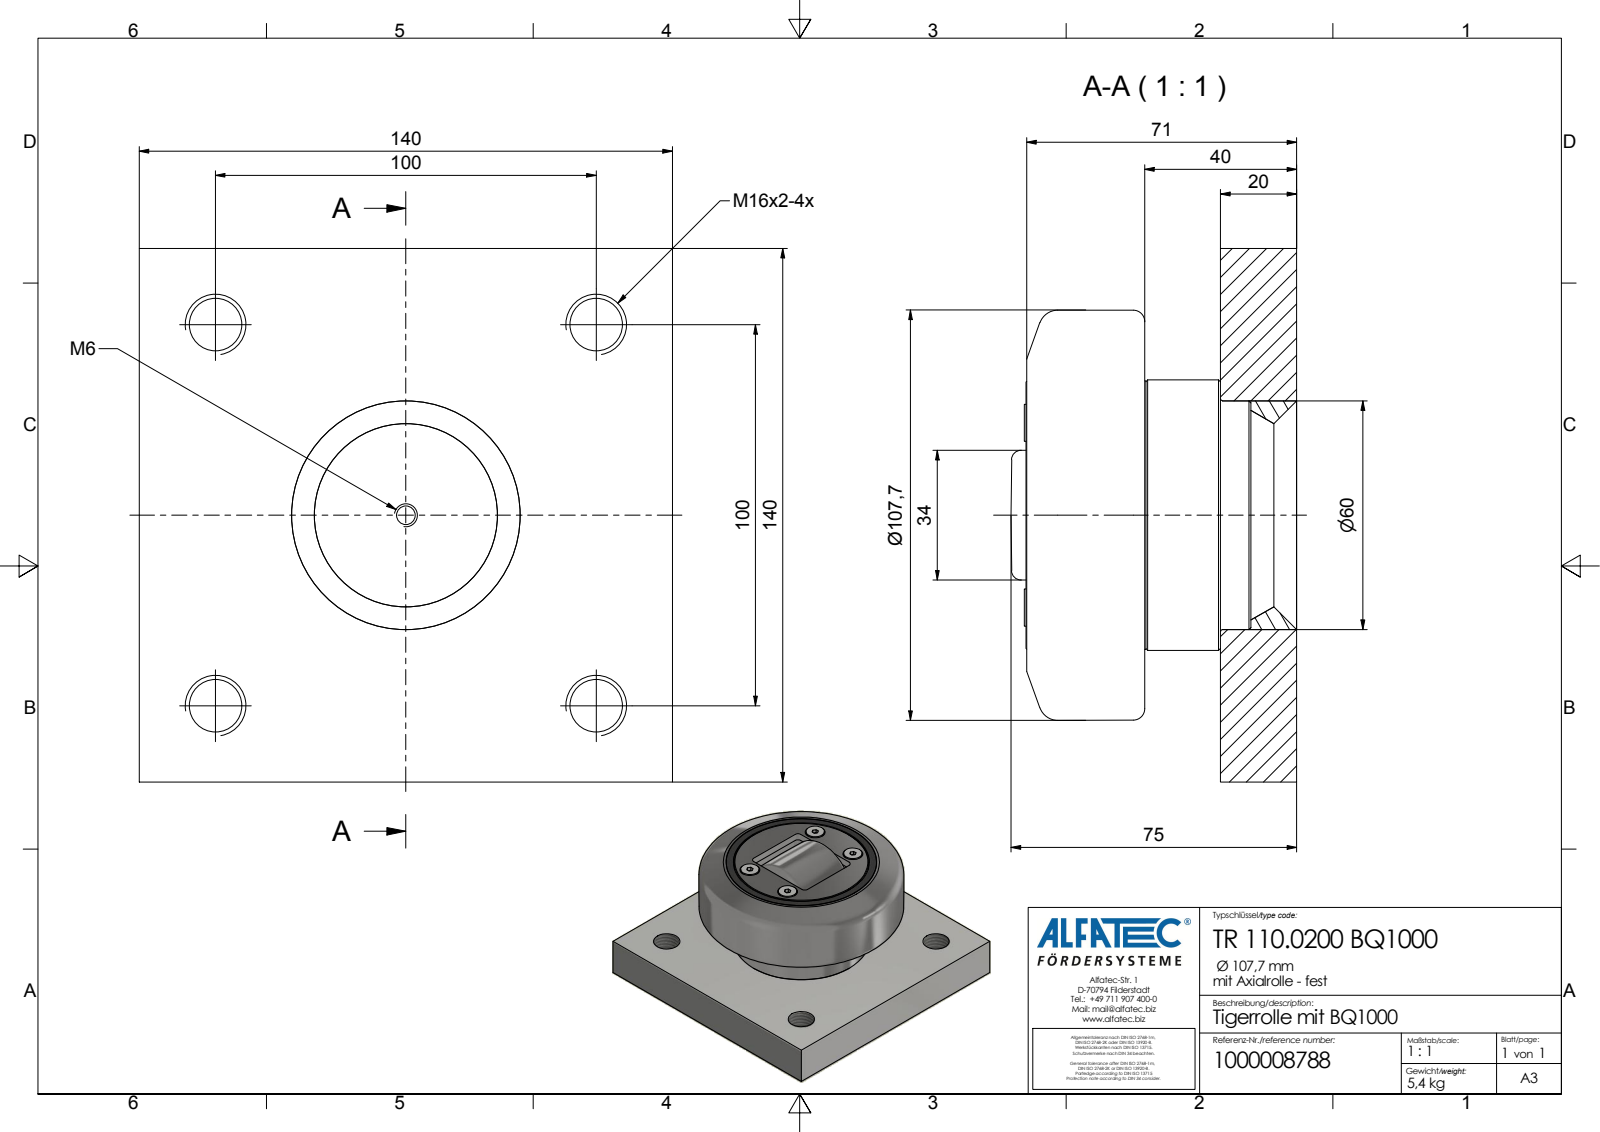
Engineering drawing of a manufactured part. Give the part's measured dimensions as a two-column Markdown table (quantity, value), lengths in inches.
| quantity | value |
| --- | --- |
| part name | TR 110.0200 BQ1000_Kontur |
| STEP written by | Autodesk Inventor 2020 (AUTOMOTIVE_DESIGN) |
| units | inches |
| bodies | 3 solids, 175 faces (74 planar, 58 cylindrical, 43 other) |
| overall size | 5.512 × 5.512 × 2.953 |
| volume | 40.28 in³ |
| surface area | 182.8 in² |
| round holes (diameter × count) | 0.118 × 4, 0.217 × 4, 0.545 × 4, 0.194 × 1, 0.791 × 1, 1.024 × 1, 1.181 × 1, 2.476 × 1, 2.48 × 1, 2.815 × 1, 3.071 × 1, 3.11 × 1 |
| round bosses / shafts (diameter × count) | 0.384 × 4, 0.197 × 4, 3.031 × 1, 2.953 × 1, 2.795 × 1, 2.776 × 1, 2.728 × 1, 2.421 × 1 |
| partial cylindrical surfaces (radius × count) | 0.079 × 8, 0.059 × 2, 0.866 × 1 |
| main face-to-face distances | 0.787, 5.512, 0.157, 1.571, 0.783, 0.256, 0.236, 2.799, 2.012, 1.228 |
| hole center spacings | 1.102, 1.743, 2.716, 2.784, 3.249, 3.859, 3.937, 1.909 |
